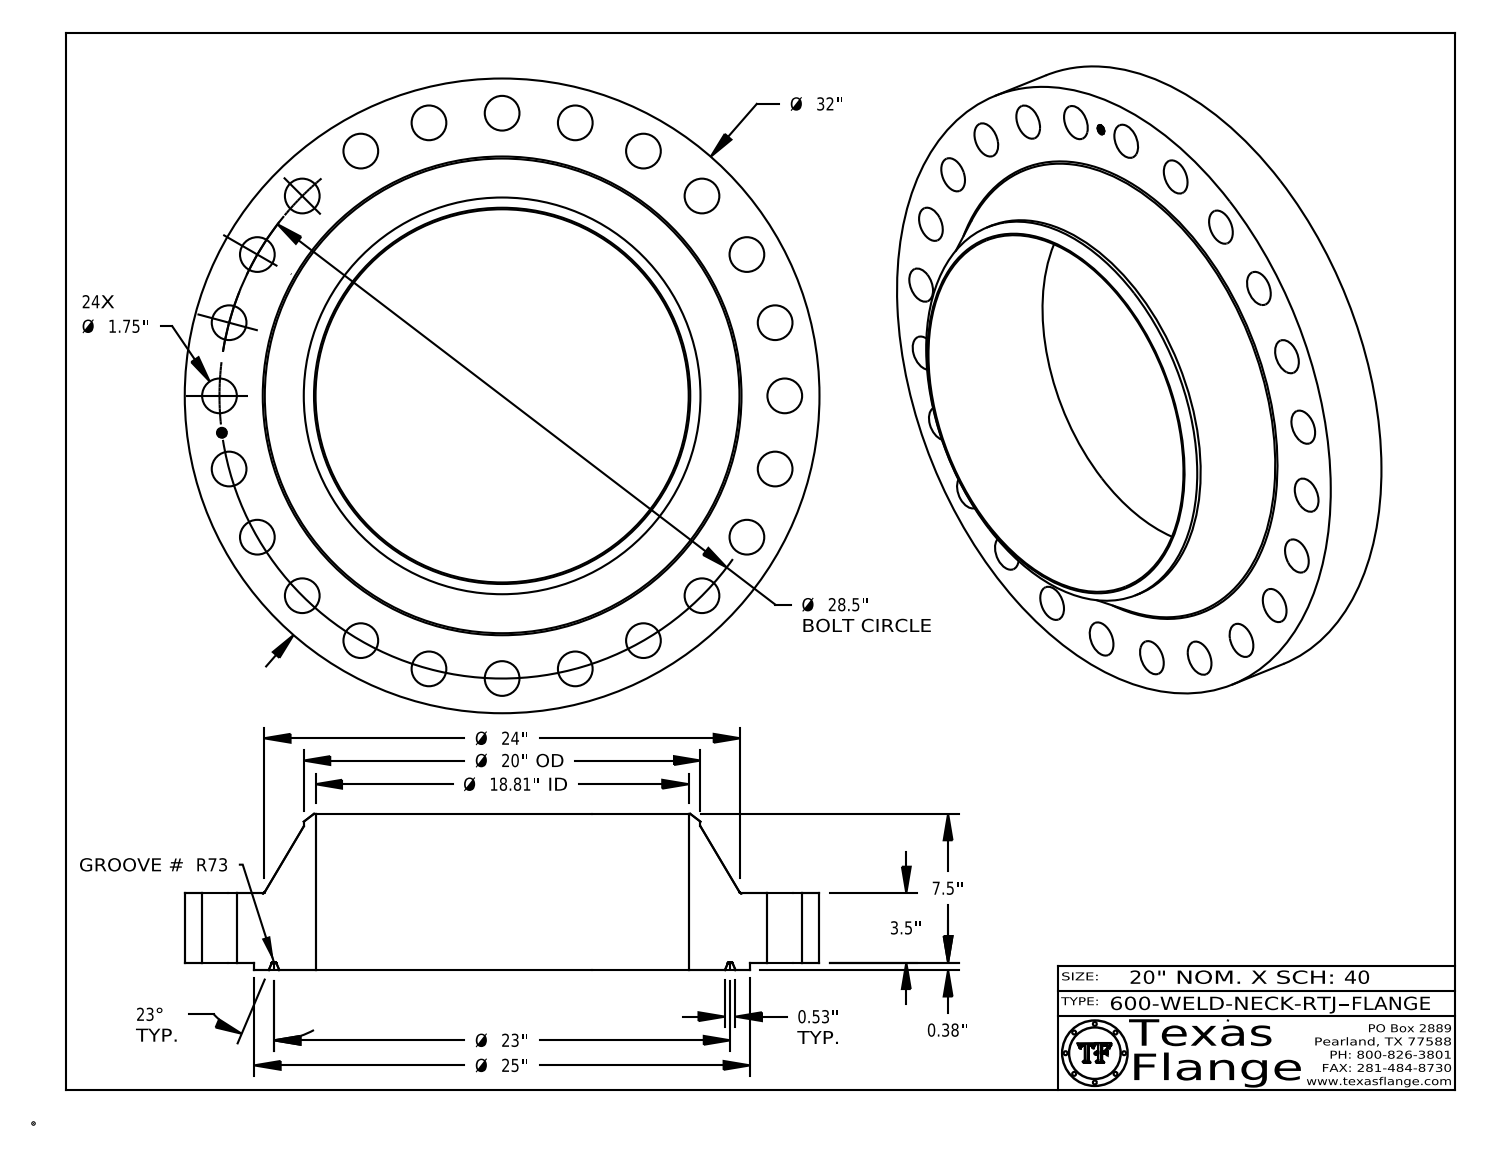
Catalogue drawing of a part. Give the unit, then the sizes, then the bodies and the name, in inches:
Units: inches
Overall size (bounding box): 32 × 32 × 7.875
Round holes (diameter × count): ⌀1.75 ×24, ⌀0.495 ×1, ⌀18.812 ×1
Round bosses / shafts (diameter × count): ⌀0.03 ×8, ⌀32 ×1, ⌀25 ×1, ⌀20 ×1, ⌀0.39 ×1
Main face-to-face distances: 3.5, 0.375, 3.875, 7.875, 7.5, 4, 0.015, 3.86, 3.485, 4.015
Hole centre spacings: 14.25, 3.72, 7.376, 24.682, 26.331, 27.529, 20.153, 10.907
Volume: 2 074 in³ · Surface area: 2 435 in²
Bodies: 1 solid, 461 faces (371 planar, 76 cylindrical, 14 other)
Part name (STEP PRODUCT): 600-WELD-NECK-RTJ
STEP written by: CATIA V5 STEP AP214 (AUTOMOTIVE_DESIGN)
